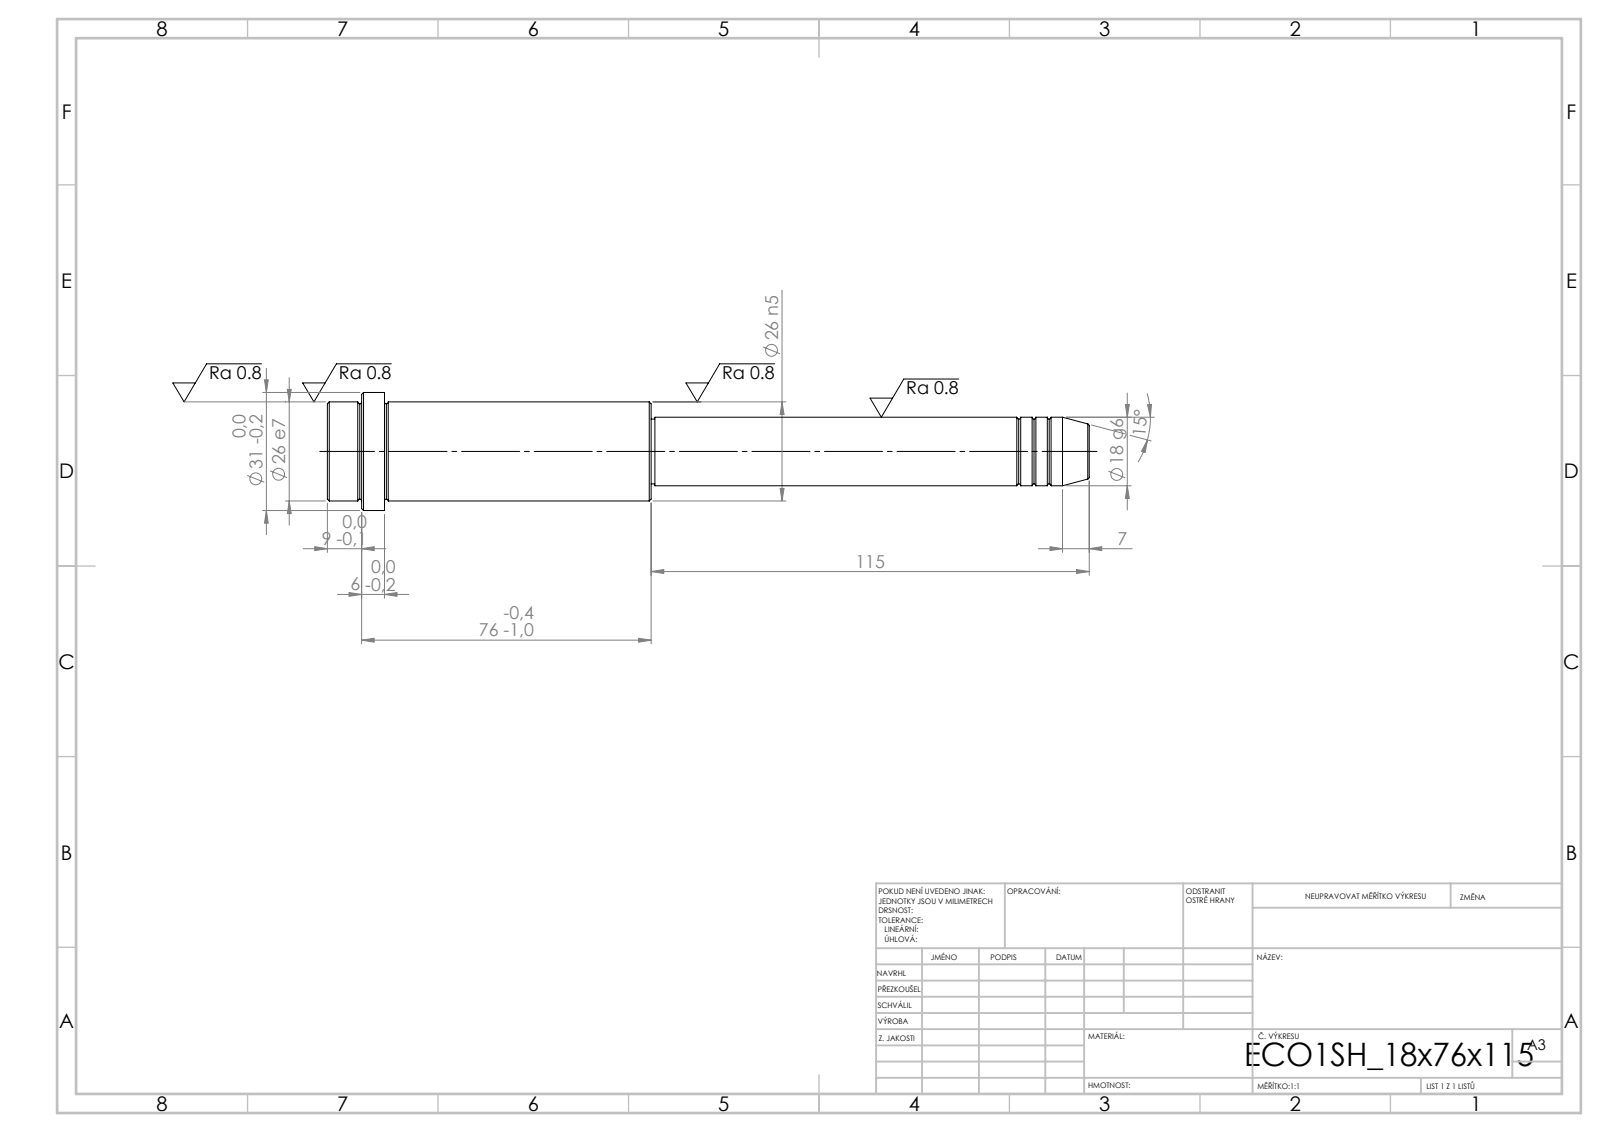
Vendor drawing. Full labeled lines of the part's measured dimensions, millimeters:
STEP written by: SolidWorks 2019 (CONFIG_CONTROL_DESIGN)
Units: millimetres
Bodies: 1 solid, 52 faces (6 planar, 16 cylindrical, 30 other)
Overall size (bounding box): 200 × 31 × 31
Volume: 75 201 mm³ · Surface area: 15 070 mm²
Round bosses / shafts (diameter × count): ⌀31 ×1, ⌀26 ×1, ⌀18 ×1, ⌀17 ×1
Main face-to-face distances: 85, 70, 15, 76, 6, 9, 115, 185, 191, 200
